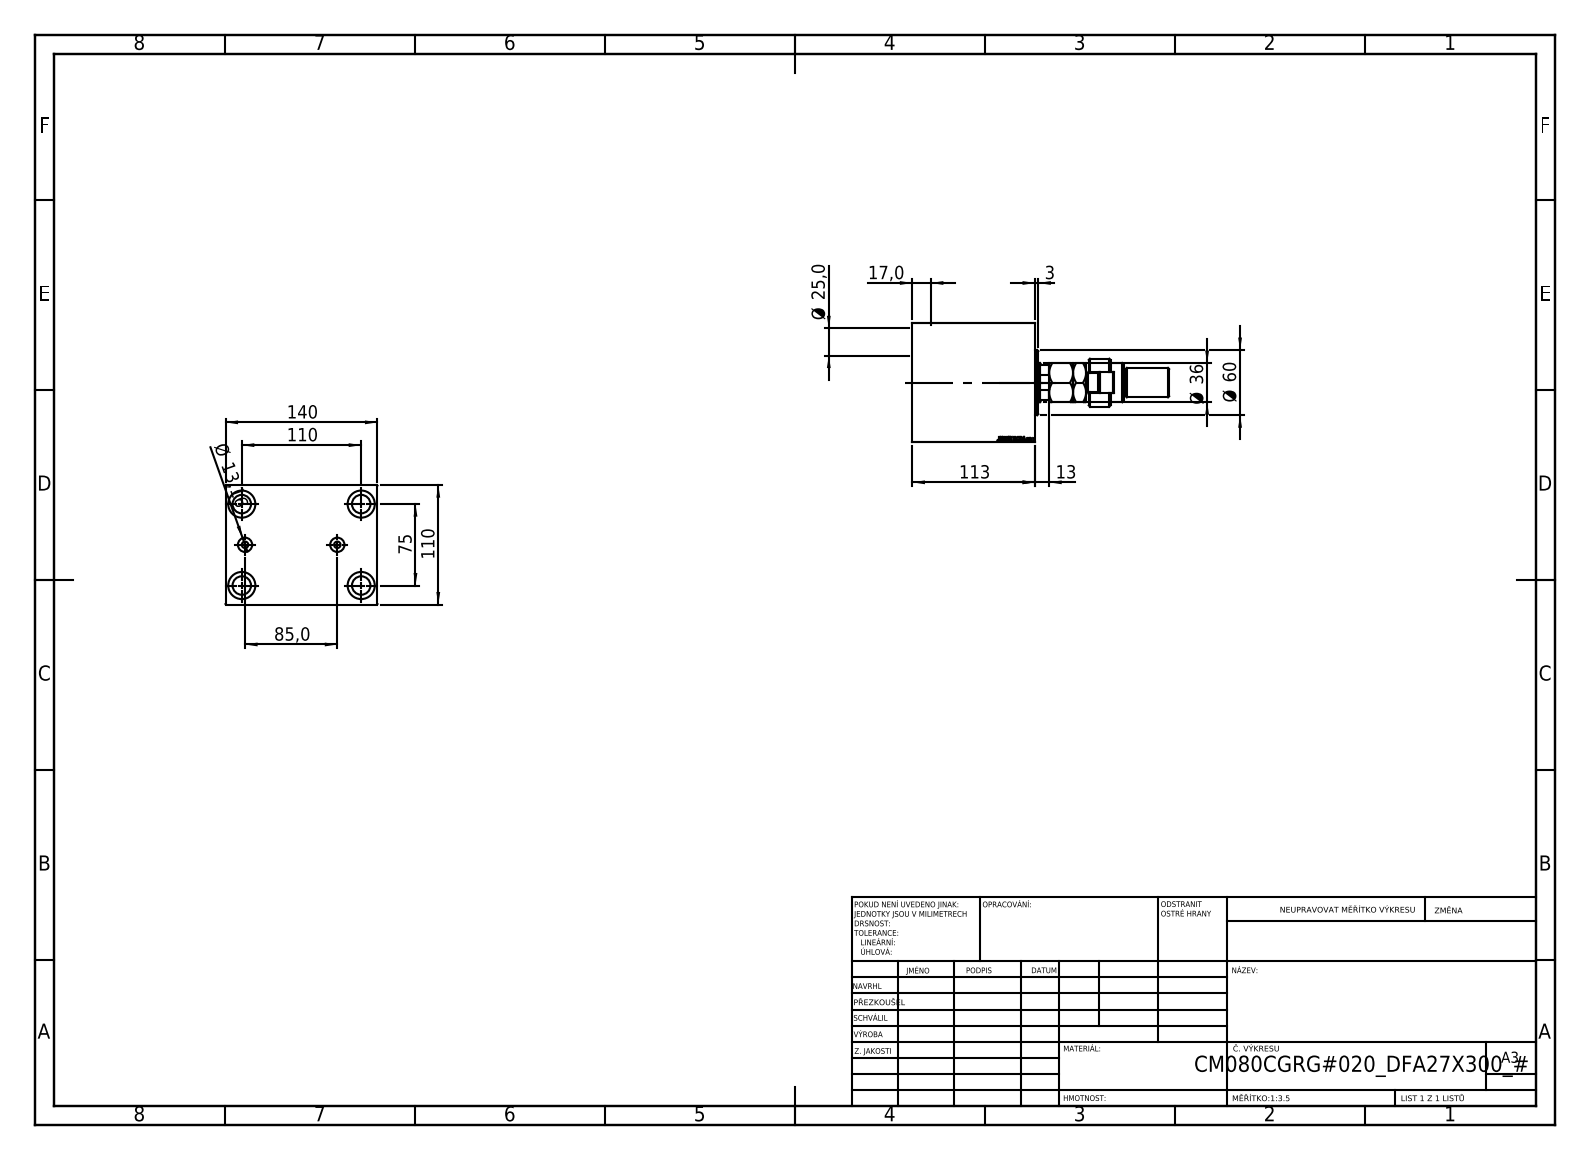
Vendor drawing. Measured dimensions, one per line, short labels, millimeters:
name: V450CM_VC_B; V450CM_C_Body; FEMALE_PART_FOR_DFA; MFA (+1 more)
written by: SolidWorks 2019 (CONFIG_CONTROL_DESIGN)
unit: mm
bodies: 5 solids, 945 faces (436 planar, 71 cylindrical, 438 other)
size: 236.5 × 140 × 110
volume: 1 653 000 mm³; area: 191 925 mm²
holes: 4× ⌀17, 4× ⌀25, 2× ⌀6, 2× ⌀13.16, 1× ⌀25.5, 1× ⌀39.5, 1× ⌀80, 1× ⌀82, 1× ⌀87
bosses: 1× ⌀60, 1× ⌀44, 1× ⌀36, 1× ⌀28, 1× ⌀27, 1× ⌀25, 1× ⌀18
rounds: 1× R9.5, 1× R15, 1× R17.5
face distances: 110, 140, 51, 113, 62, 10, 21.6, 29.4, 91.4, 81.4
hole spacings: 66.57, 37.62, 43.48, 75, 95.66, 110, 113.38, 133.14
